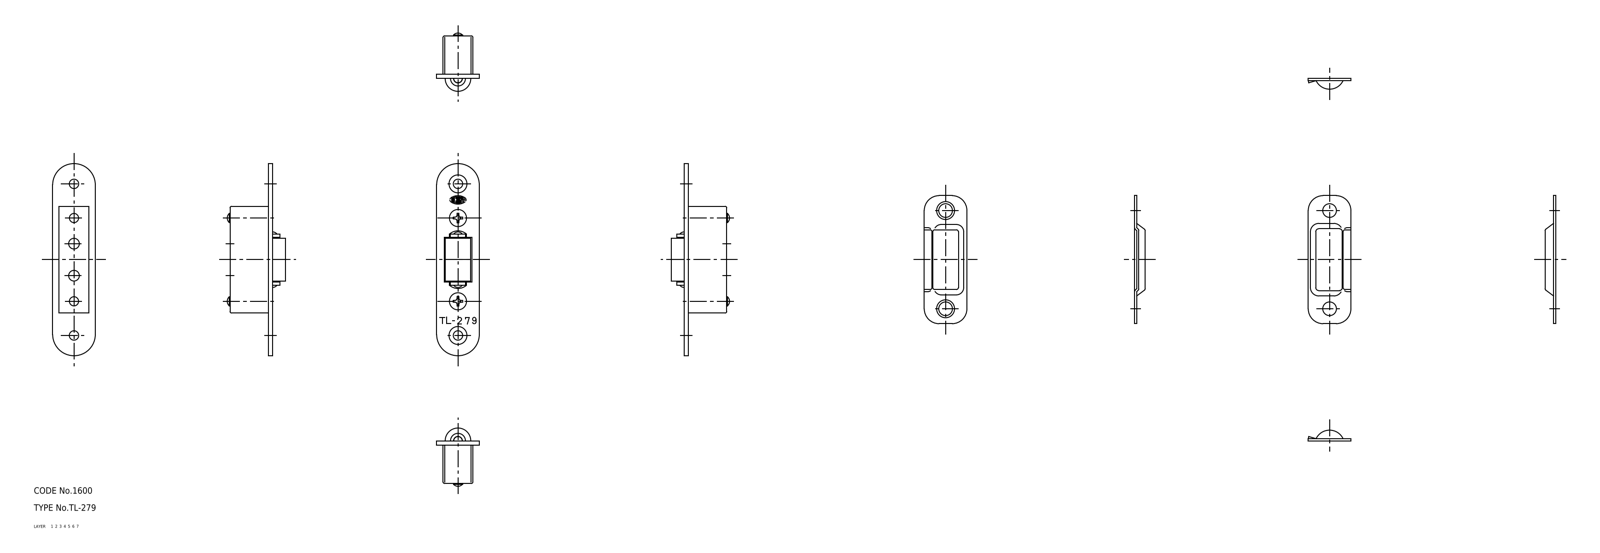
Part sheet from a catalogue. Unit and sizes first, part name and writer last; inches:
Units: inches
Overall size (bounding box): 3.543 × 2.955 × 0.787
Volume: 0.568 in³ · Surface area: 23.41 in²
Bodies: 10 solids, 207 faces (0 planar, 0 cylindrical, 207 other)
Part name (STEP PRODUCT): 67119970; 67119983; 67119996; 67120009 (+6 more)
STEP written by: CADfix (AUTOMOTIVE_DESIGN)
